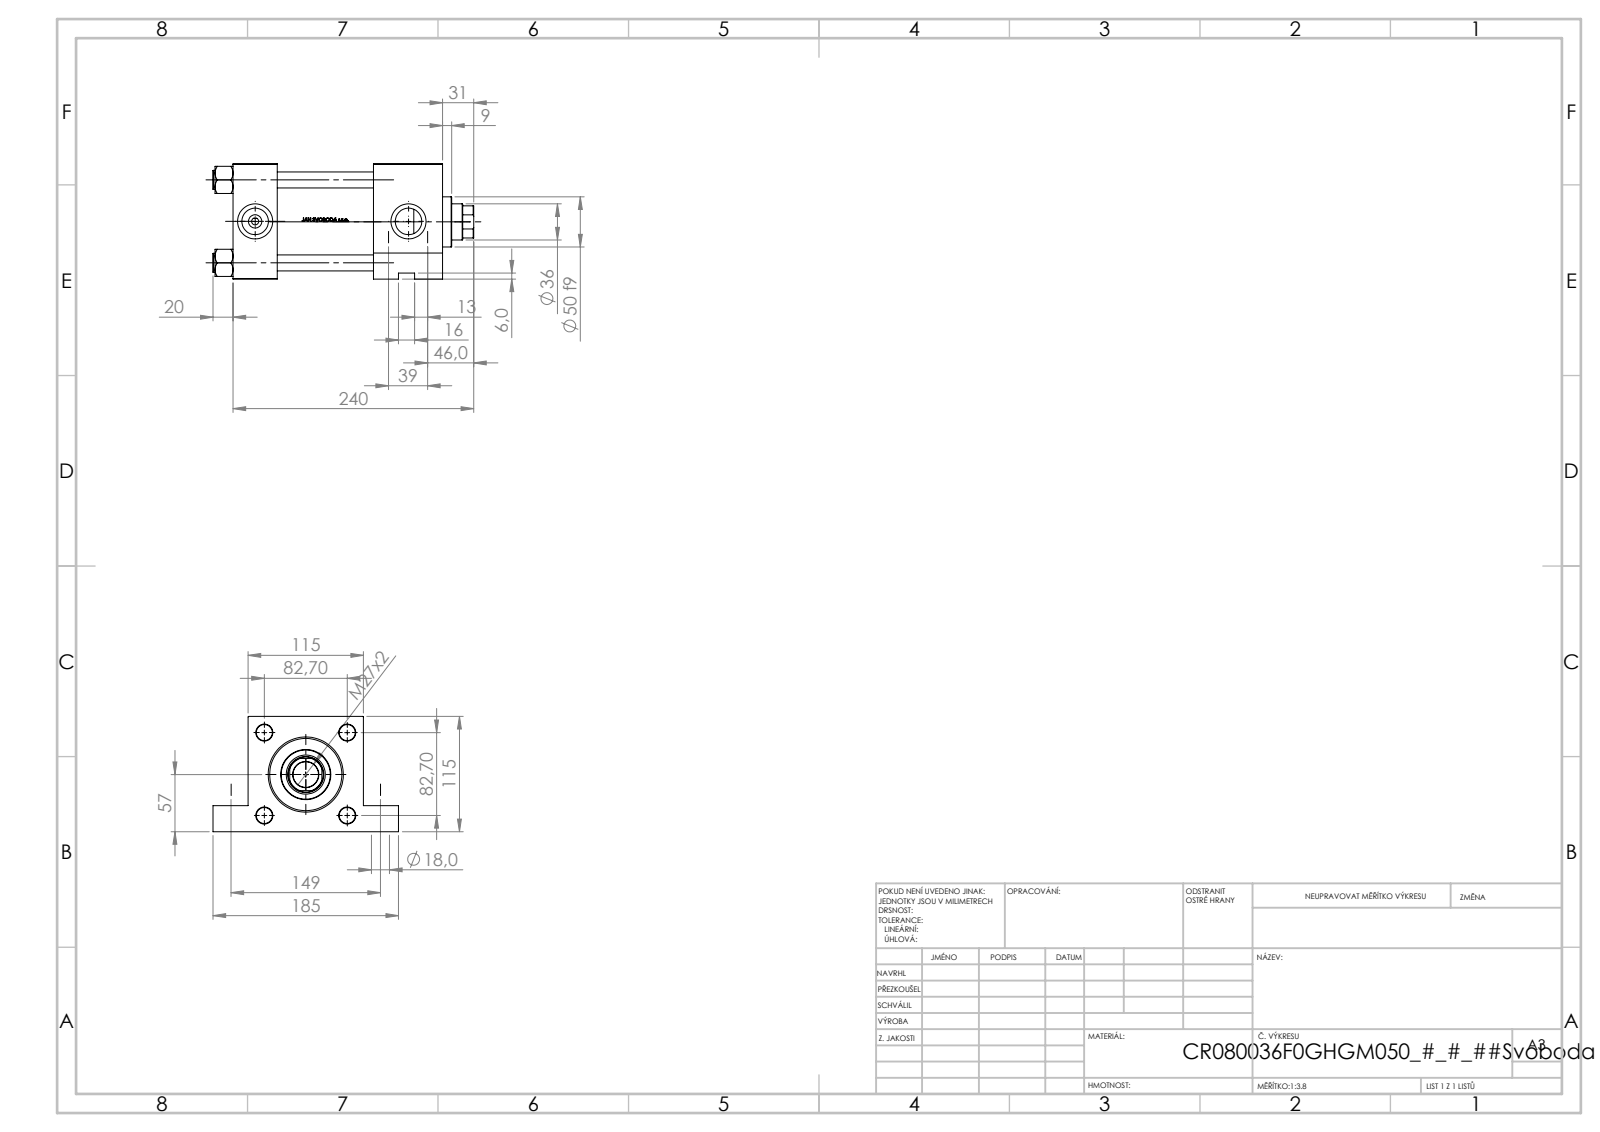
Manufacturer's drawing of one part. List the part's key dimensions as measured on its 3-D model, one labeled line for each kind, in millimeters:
Part name (STEP PRODUCT): V215CR_VCP_F; V215CR_F_TYCINKA; V215CR_F_Body; NUT_M5_F (+1 more)
STEP written by: SolidWorks 2019 (CONFIG_CONTROL_DESIGN)
Units: millimetres
Bodies: 11 solids, 1151 faces (485 planar, 126 cylindrical, 540 other)
Overall size (bounding box): 260 × 185 × 115
Volume: 1 961 000 mm³ · Surface area: 308 647 mm²
Round holes (diameter × count): ⌀16 ×4, ⌀18 ×4, ⌀7 ×2, ⌀26.44 ×2, ⌀35 ×2, ⌀25.5 ×1, ⌀36 ×1, ⌀39 ×1, ⌀61 ×1, ⌀72 ×1, ⌀80 ×1
Round bosses / shafts (diameter × count): ⌀19 ×4, ⌀86 ×1, ⌀50 ×1
Partial cylindrical surfaces — rounded edges, fillets, slot ends (radius × count): R17.5 ×1
Main face-to-face distances: 115, 44, 165, 209, 140, 96, 69, 109, 180.3, 136.3
Hole centre spacings: 82.7, 39, 58.13, 58.83, 116.96, 149, 154.02, 153
